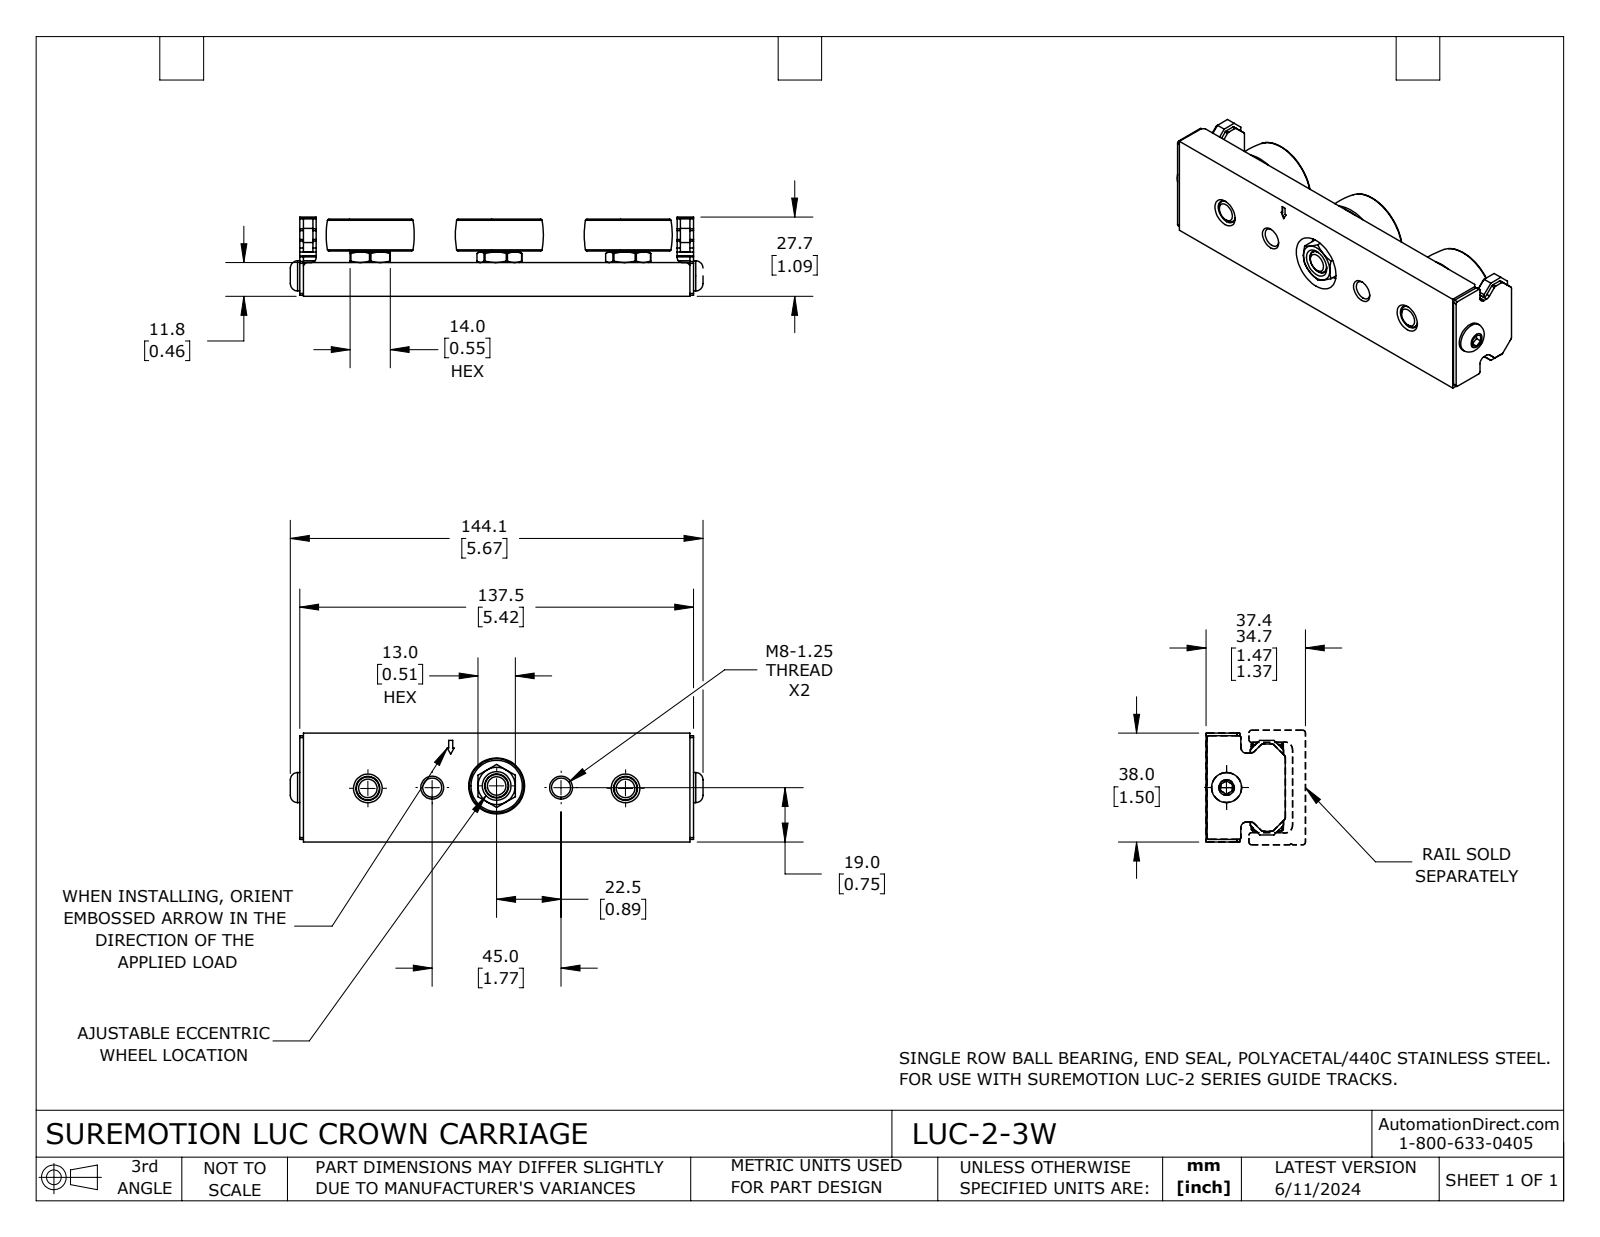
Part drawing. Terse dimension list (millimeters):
name: LUC-2-3W
written by: SolidWorks 2023 (CONFIG_CONTROL_DESIGN)
unit: mm
bodies: 7 solids, 529 faces (229 planar, 150 cylindrical, 150 other)
size: 144.14 × 38 × 27.69
volume: 87 700 mm³; area: 32 156 mm²
holes: 3× ⌀8.38, 3× ⌀19, 2× ⌀6.65, 1× ⌀4.92, 1× ⌀9.59, 1× ⌀19.56
bosses: 3× ⌀9.33, 3× ⌀8, 3× ⌀6.3, 2× ⌀9.53, 1× ⌀17.91, 1× ⌀10.5, 1× ⌀9.52, 1× ⌀6
rounds: 12× R0.64, 6× R0.38, 6× R0.84, 4× R1.98, 3× R7.95, 2× R1.78
face distances: 11.79, 38, 1.27, 136.27, 1.86, 9.27, 4.06, 26.98, 15.19, 11.13
hole spacings: 0.97, 22.51, 45.01, 0.96, 21.56, 21.64, 22.48, 22.52
